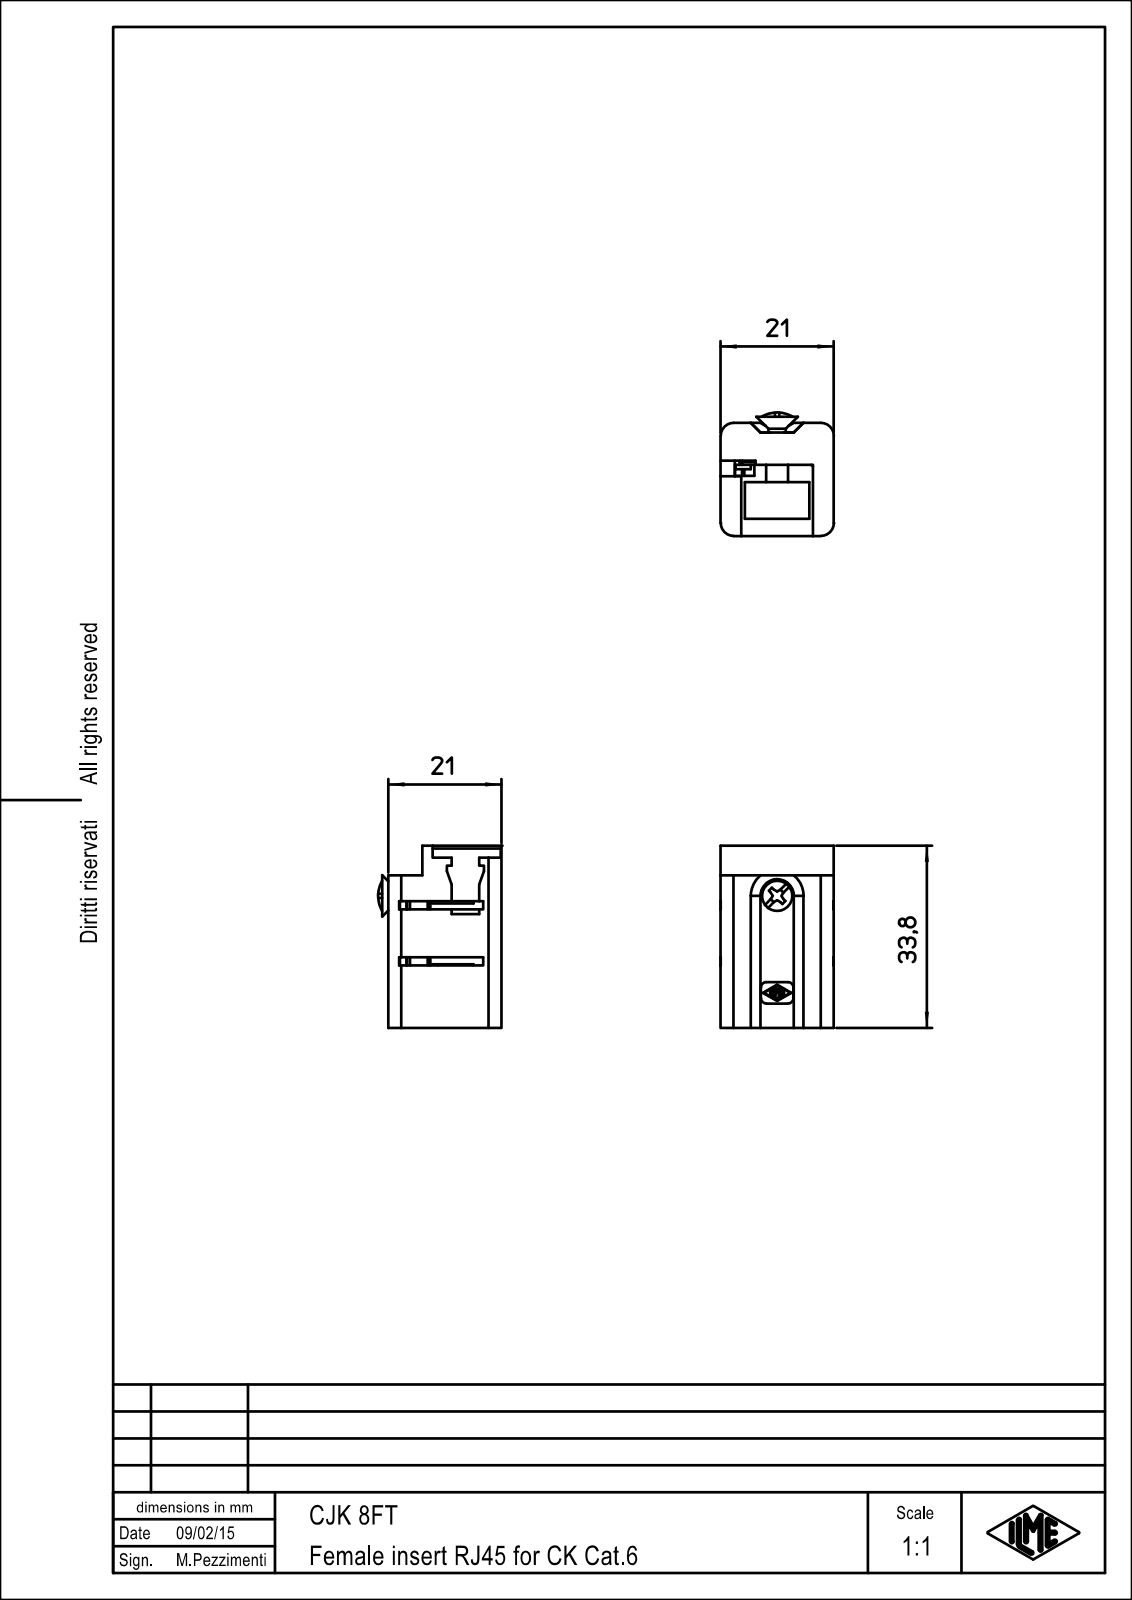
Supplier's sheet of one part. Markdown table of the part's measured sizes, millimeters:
| quantity | value |
| --- | --- |
| part name | CJK_8FT |
| STEP written by | PTC Creo Elements/Direct Modeling 19.0B 21-Mar-2015 (C) Parametric Technology GmbH (AUTOMOTIVE_DESIGN) |
| units | millimeters |
| bodies | 1 solid, 262 faces (202 planar, 33 cylindrical, 27 other) |
| overall size | 33.8 × 24.89 × 21 |
| volume | 8 780 mm³ |
| surface area | 8 070 mm² |
| round bosses / shafts (diameter × count) | 5.6 × 1, 3 × 1 |
| partial cylindrical surfaces (radius × count) | 0.1 × 15, 1 × 4, 2.4 × 4, 0.2 × 1, 3.5 × 1 |
| main face-to-face distances | 2.7, 15.65, 2.65, 18.35, 18.3, 10, 3.2, 21, 15.7, 1.5 |
